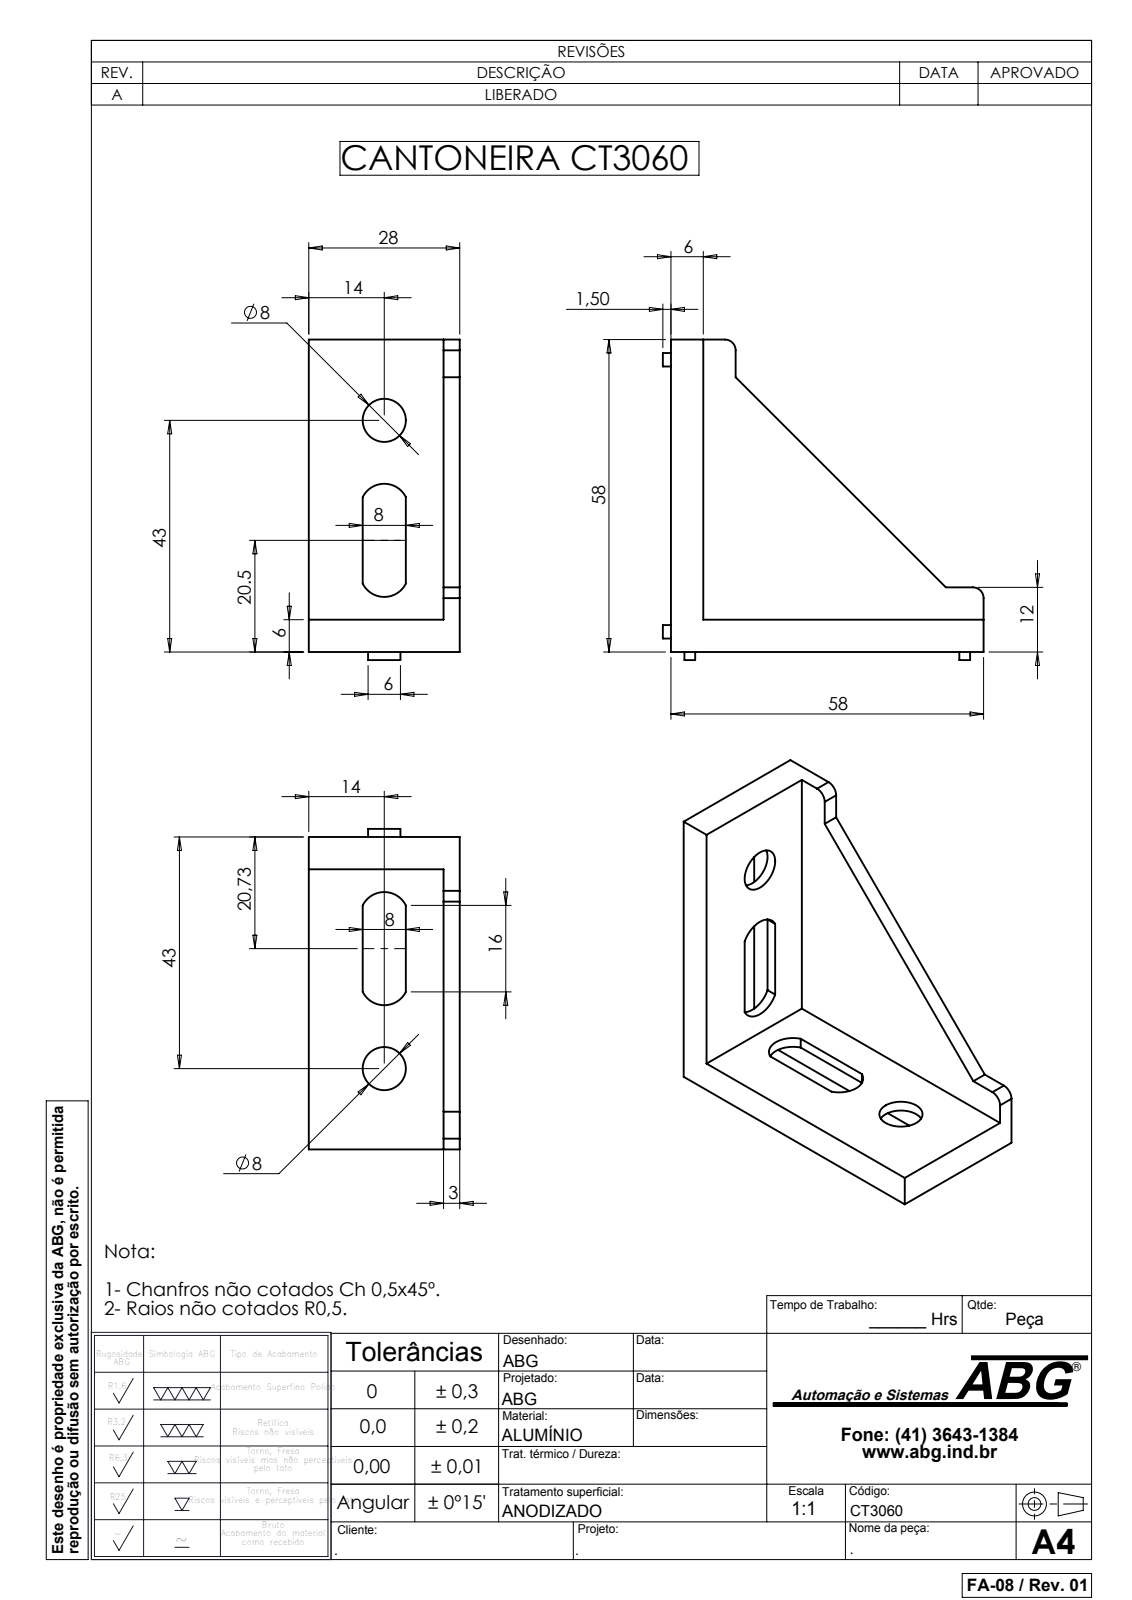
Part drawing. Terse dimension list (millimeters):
name: CT3060
written by: SolidWorks 2007 (CONFIG_CONTROL_DESIGN)
unit: mm
bodies: 1 solid, 69 faces (58 planar, 11 cylindrical, 0 other)
size: 59.5 × 59.5 × 28
volume: 14 204 mm³; area: 12 706 mm²
holes: 2× ⌀8
rounds: 4× R4.47, 2× R2
face distances: 3, 2, 6, 4, 25, 1.5, 5, 8, 17, 20
